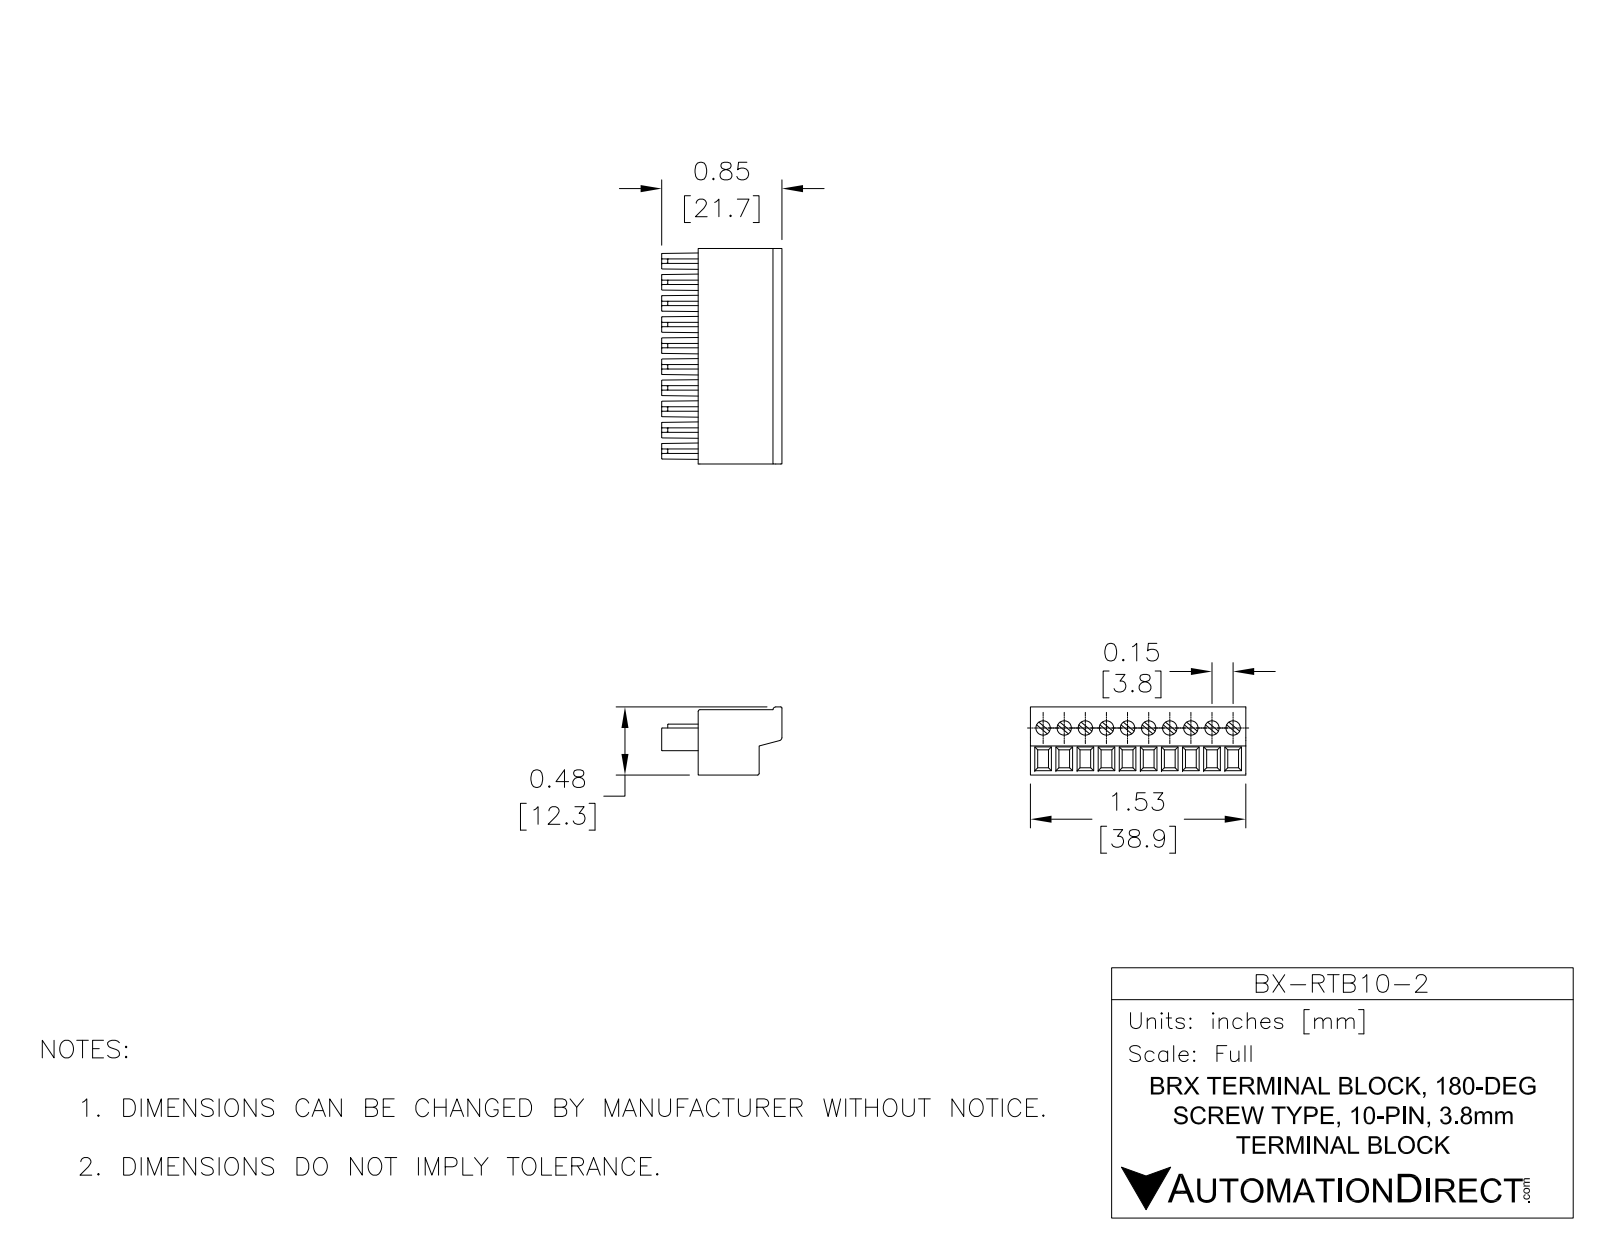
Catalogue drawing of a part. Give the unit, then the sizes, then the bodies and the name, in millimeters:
Units: millimetres
Overall size (bounding box): 38.89 × 21.7 × 12.3
Round holes (diameter × count): ⌀1.6 ×10, ⌀2.6 ×10
Partial cylindrical surfaces — rounded edges, fillets, slot ends (radius × count): R0.1 ×145, R0.3 ×20, R1.83 ×10, R0.3 ×2, R0.5 ×2, R0.2 ×1
Main face-to-face distances: 3.81, 7.62, 11.8, 11.43, 15.24, 19.05, 22.86, 26.67, 15.1, 38.89
Hole centre spacings: 3.81, 4.26, 7.62, 7.85, 11.43, 11.59, 15.24, 15.36
Volume: 6 228 mm³ · Surface area: 4 278 mm²
Bodies: 1 solid, 674 faces (259 planar, 285 cylindrical, 130 other)
Part name (STEP PRODUCT): BX-RTB10-2
STEP written by: SolidWorks 2016 (AUTOMOTIVE_DESIGN)
